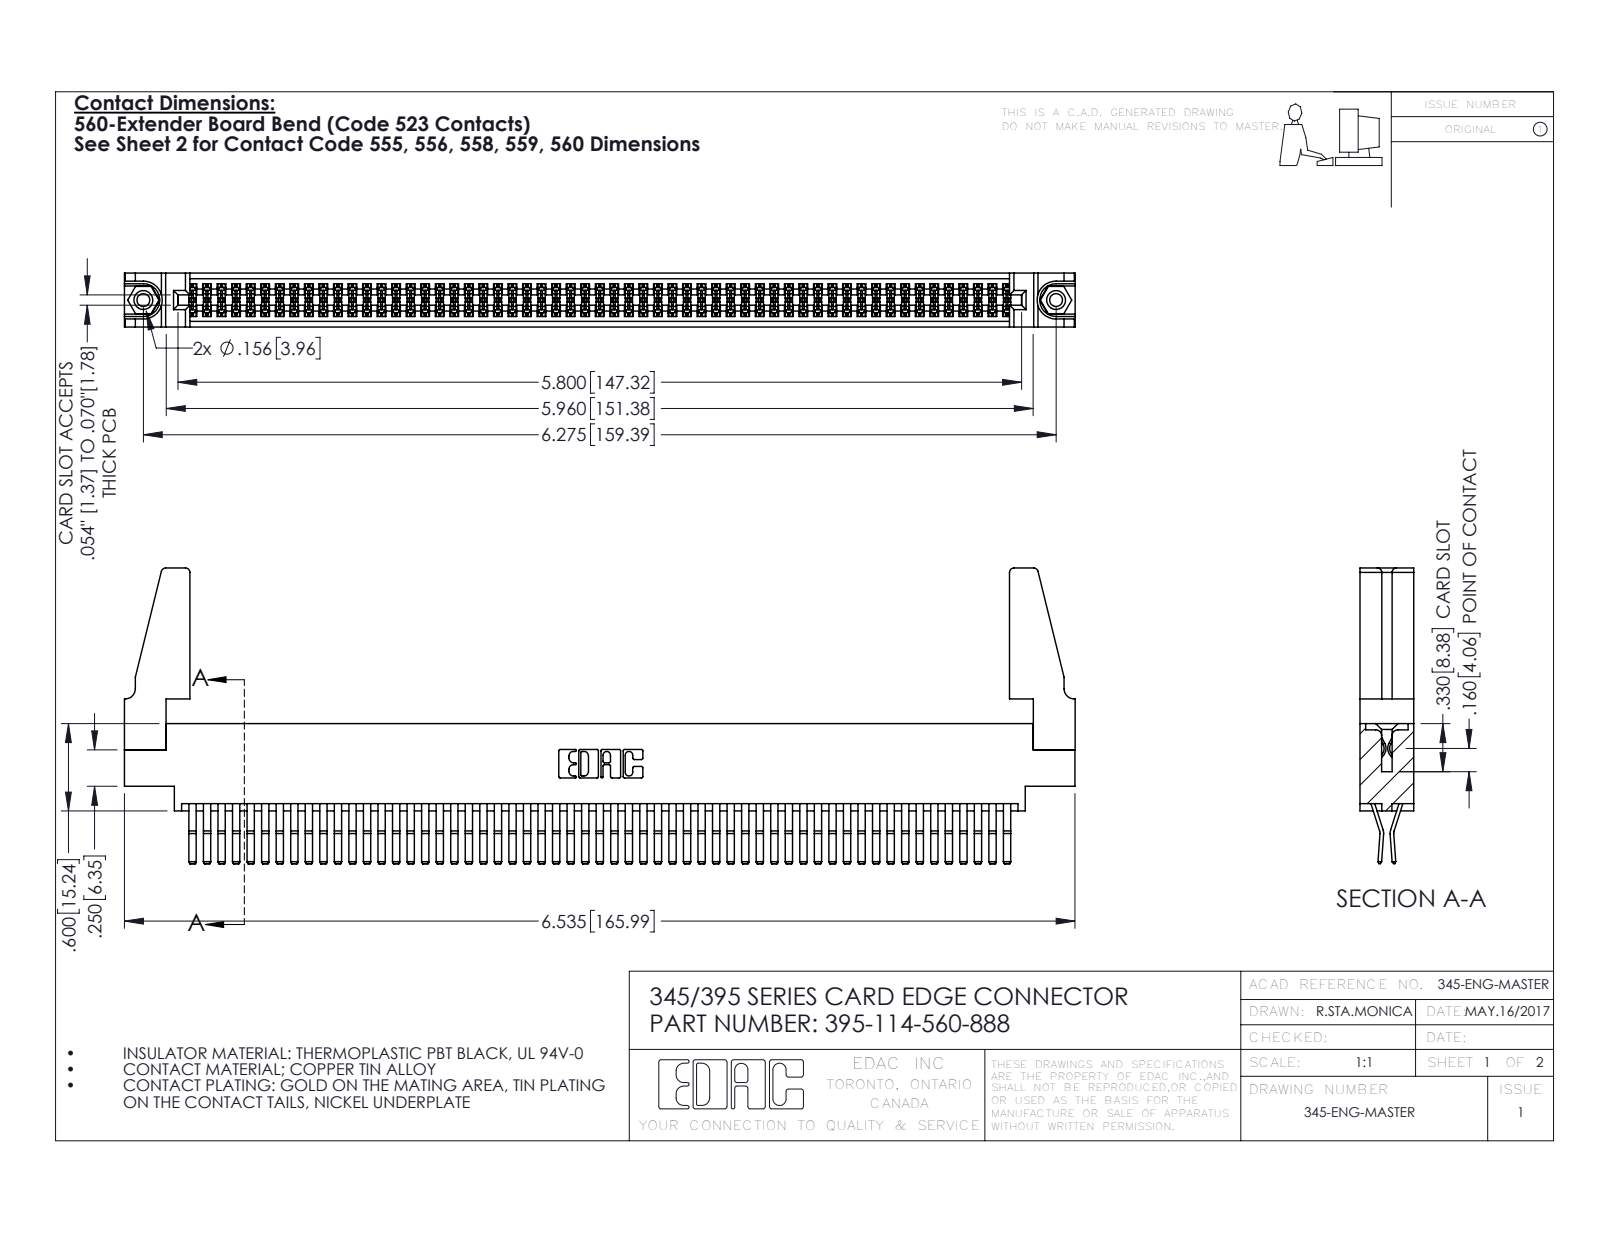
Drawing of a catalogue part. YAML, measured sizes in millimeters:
part_name: "345-292-001_560 Tail; 395-114-560-888; 345-220-078_345-220-088; 345 Part_0.170 Offset - 0.156 Dia-TH (+1 more)"
step_written_by: "SolidWorks 2016 (CONFIG_CONTROL_DESIGN)"
units: millimeters
bodies: {solids: 119, faces: 6182, planar: 3918, cylindrical: 2248, other: 16}
overall_size: [166, 51.6, 9.4]
volume: 20160
surface_area: 30460
round_holes:
  - {diameter: 2.3, count: 2}
  - {diameter: 3.2, count: 2}
  - {diameter: 4, count: 2}
  - {diameter: 1.6, count: 1}
round_bosses_or_shafts:
  - {diameter: 3.9, count: 2}
partial_cylinders:
  - {radius: 0.2, count: 172}
  - {radius: 0.3, count: 22}
  - {radius: 0.8, count: 8}
  - {radius: 0.2, count: 6}
  - {radius: 0.8, count: 6}
  - {radius: 0.7, count: 3}
  - {radius: 0.3, count: 2}
  - {radius: 0.4, count: 2}
face_to_face_distances: [1.8, 7.6, 0.6, 9.4, 5.1, 2.5, 6.9, 5.7, 4.4, 3.8]
hole_center_spacings: [6.9, 153.4, 159.4]
